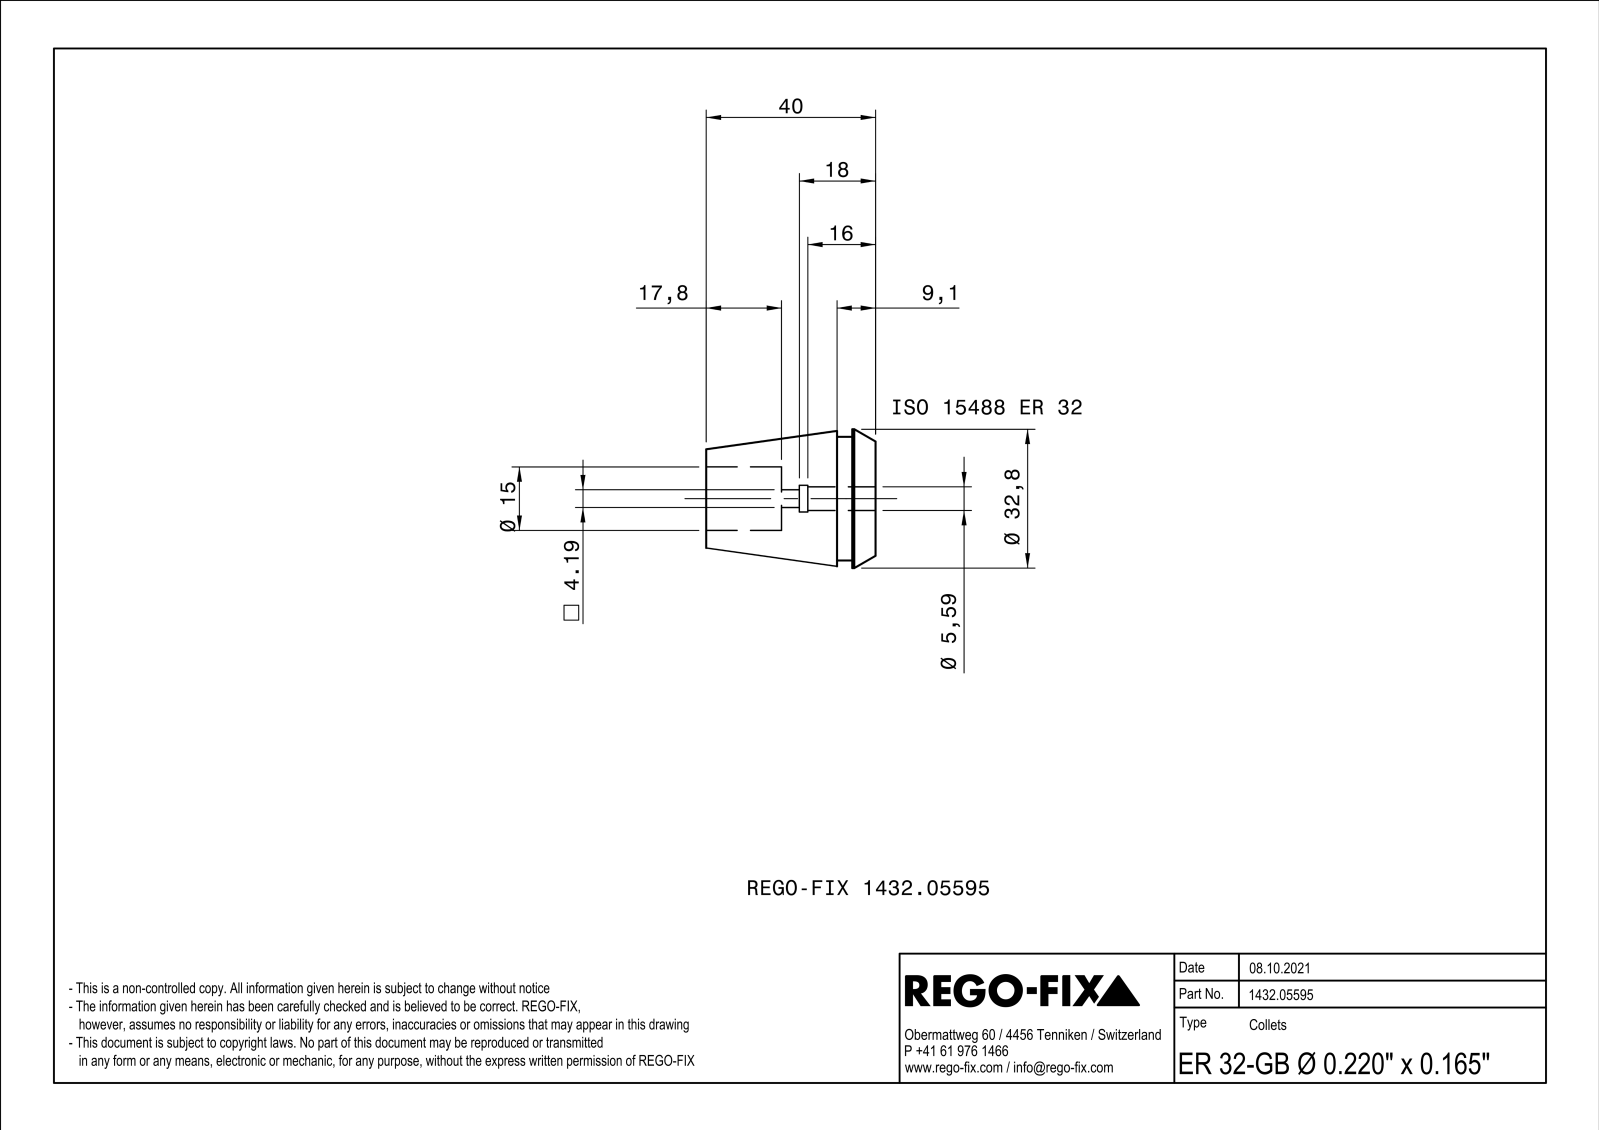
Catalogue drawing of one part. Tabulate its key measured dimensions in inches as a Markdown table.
| quantity | value |
| --- | --- |
| part name | NOCUT |
| STEP written by | SIEMENS PLM Software Solid Edge ST10 (AUTOMOTIVE_DESIGN) |
| units | inches |
| bodies | 1 solid, 168 faces (68 planar, 32 cylindrical, 68 other) |
| overall size | 1.575 × 1.291 × 1.291 |
| volume | 1.177 in³ |
| surface area | 16.68 in² |
| round holes (diameter × count) | 0.22 × 1, 0.591 × 1 |
| round bosses / shafts (diameter × count) | 1.291 × 1, 1.15 × 1 |
| partial cylindrical surfaces (radius × count) | 0.098 × 1, 0.124 × 1 |
| main face-to-face distances | 0.031, 1.575, 0.217, 1.358, 0.874, 0.657, 0.701, 0.358, 0.142, 0.516 |
